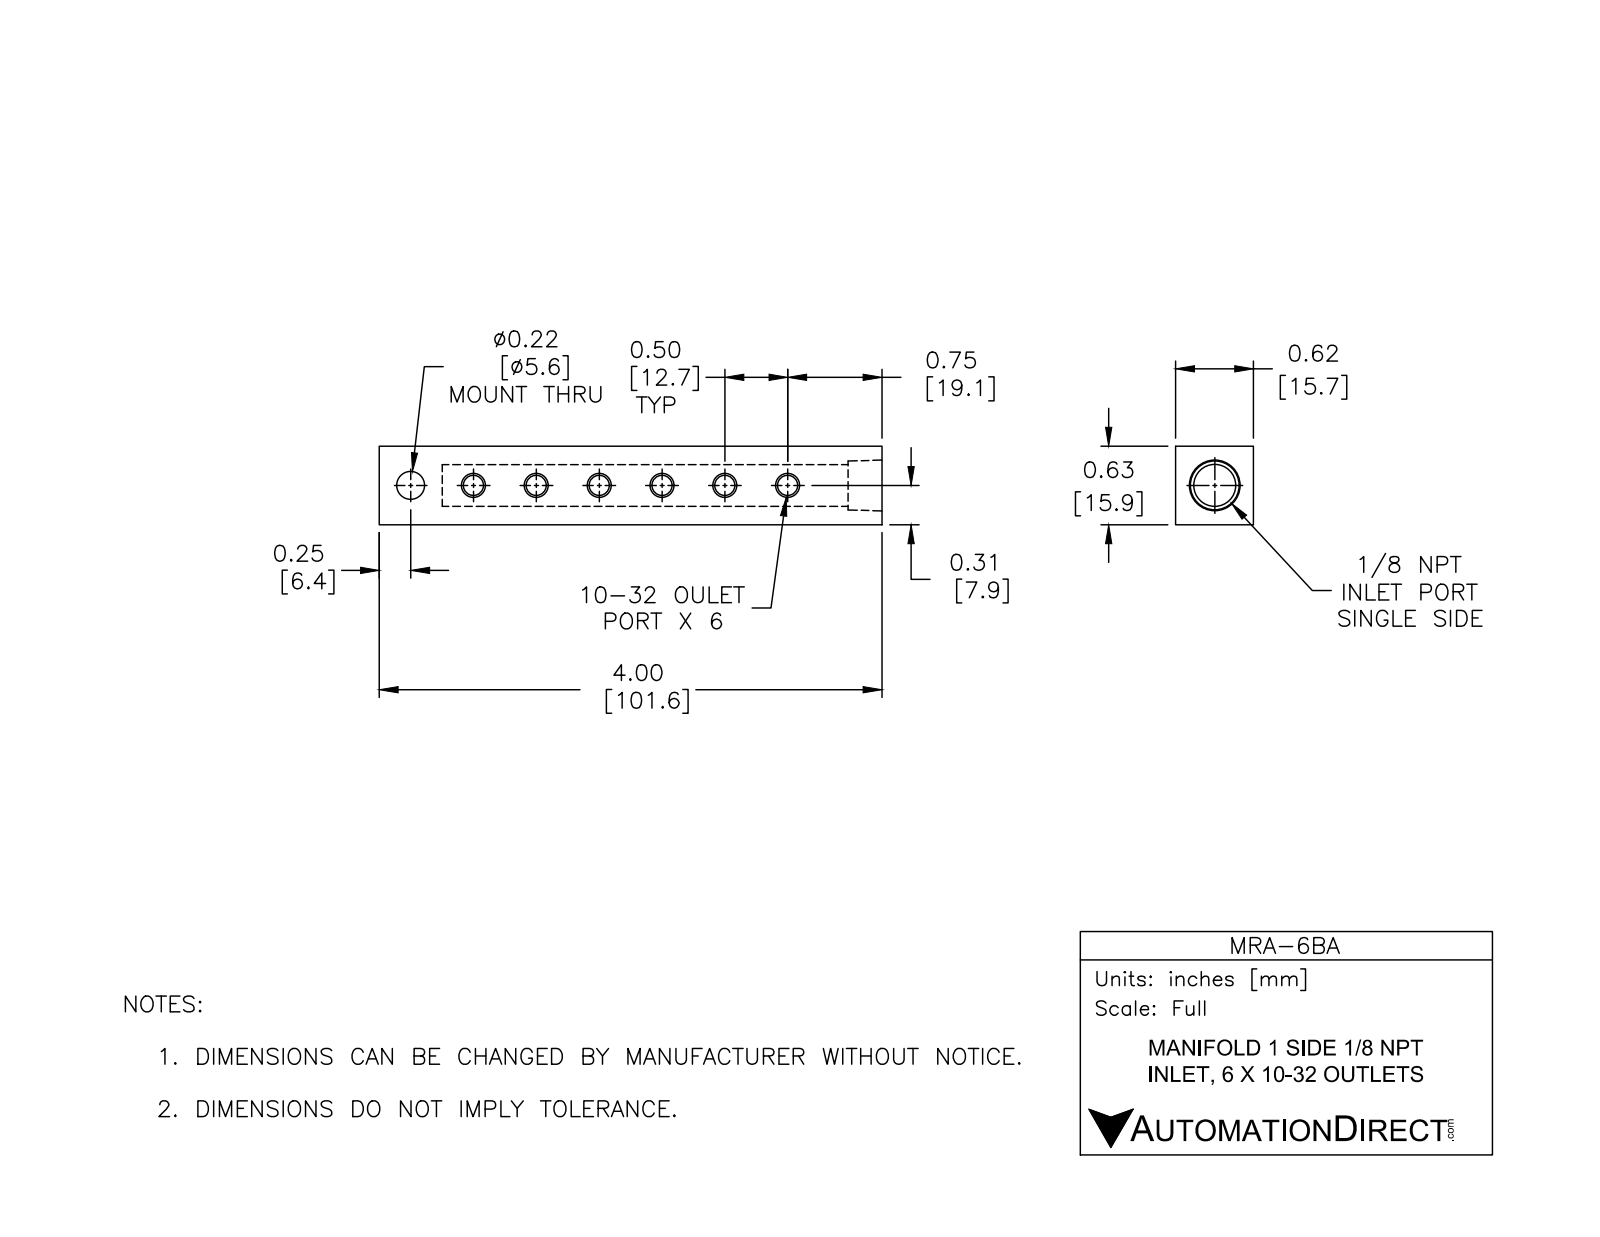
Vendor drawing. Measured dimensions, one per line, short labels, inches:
name: MRA-6BA
written by: SolidWorks 2015 (CONFIG_CONTROL_DESIGN)
unit: in
bodies: 1 solid, 26 faces (8 planar, 16 cylindrical, 2 other)
size: 4 × 0.625 × 0.62
volume: 1.195 in³; area: 15.01 in²
holes: 6× ⌀0.159, 1× ⌀0.22, 1× ⌀0.332
face distances: 0.625, 0.62, 4, 0.5, 3.5, 3.73, 3.23, 0.27
hole spacings: 0.5, 1, 1.5, 2, 2.5, 3
